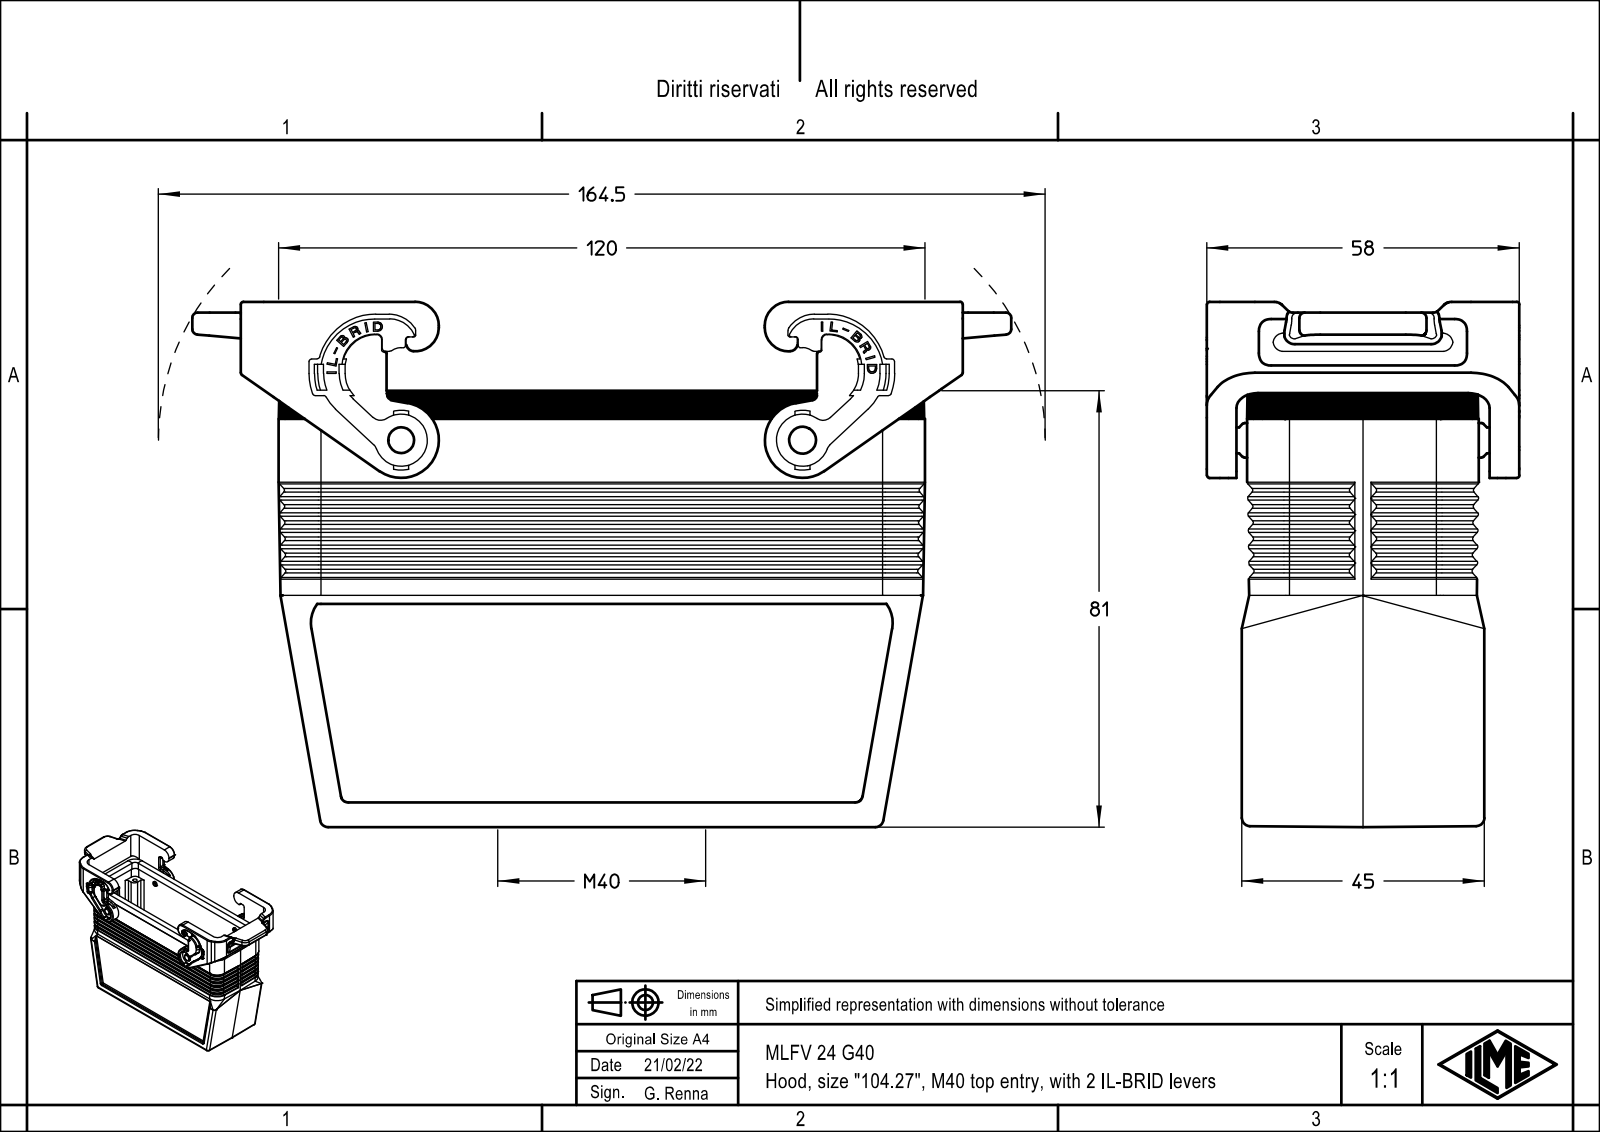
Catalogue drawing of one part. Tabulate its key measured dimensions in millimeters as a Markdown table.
| quantity | value |
| --- | --- |
| part name | MLFV_24_G40 |
| STEP written by | Creo Elements/Direct Modeling 20.1B 02-Apr-2019 (C) Parametric Technology GmbH (AUTOMOTIVE_DESIGN) |
| units | millimeters |
| bodies | 1 solid, 1602 faces (1031 planar, 391 cylindrical, 180 other) |
| overall size | 152 × 97.45 × 58 |
| volume | 134 676 mm³ |
| surface area | 71 268 mm² |
| round holes (diameter × count) | 2.75 × 4, 38.6 × 1 |
| round bosses / shafts (diameter × count) | 6.8 × 2, 4.8 × 2 |
| partial cylindrical surfaces (radius × count) | 0.5 × 104, 1 × 46, 3 × 20, 7 × 16, 0.33 × 15, 1.5 × 14, 0.3 × 8, 2 × 8 |
| main face-to-face distances | 39.25, 3.75, 2, 1, 43, 4.75, 5.75, 35.5, 38.25, 34.5 |
| hole center spacings | 53.72, 27, 104, 107.45 |
